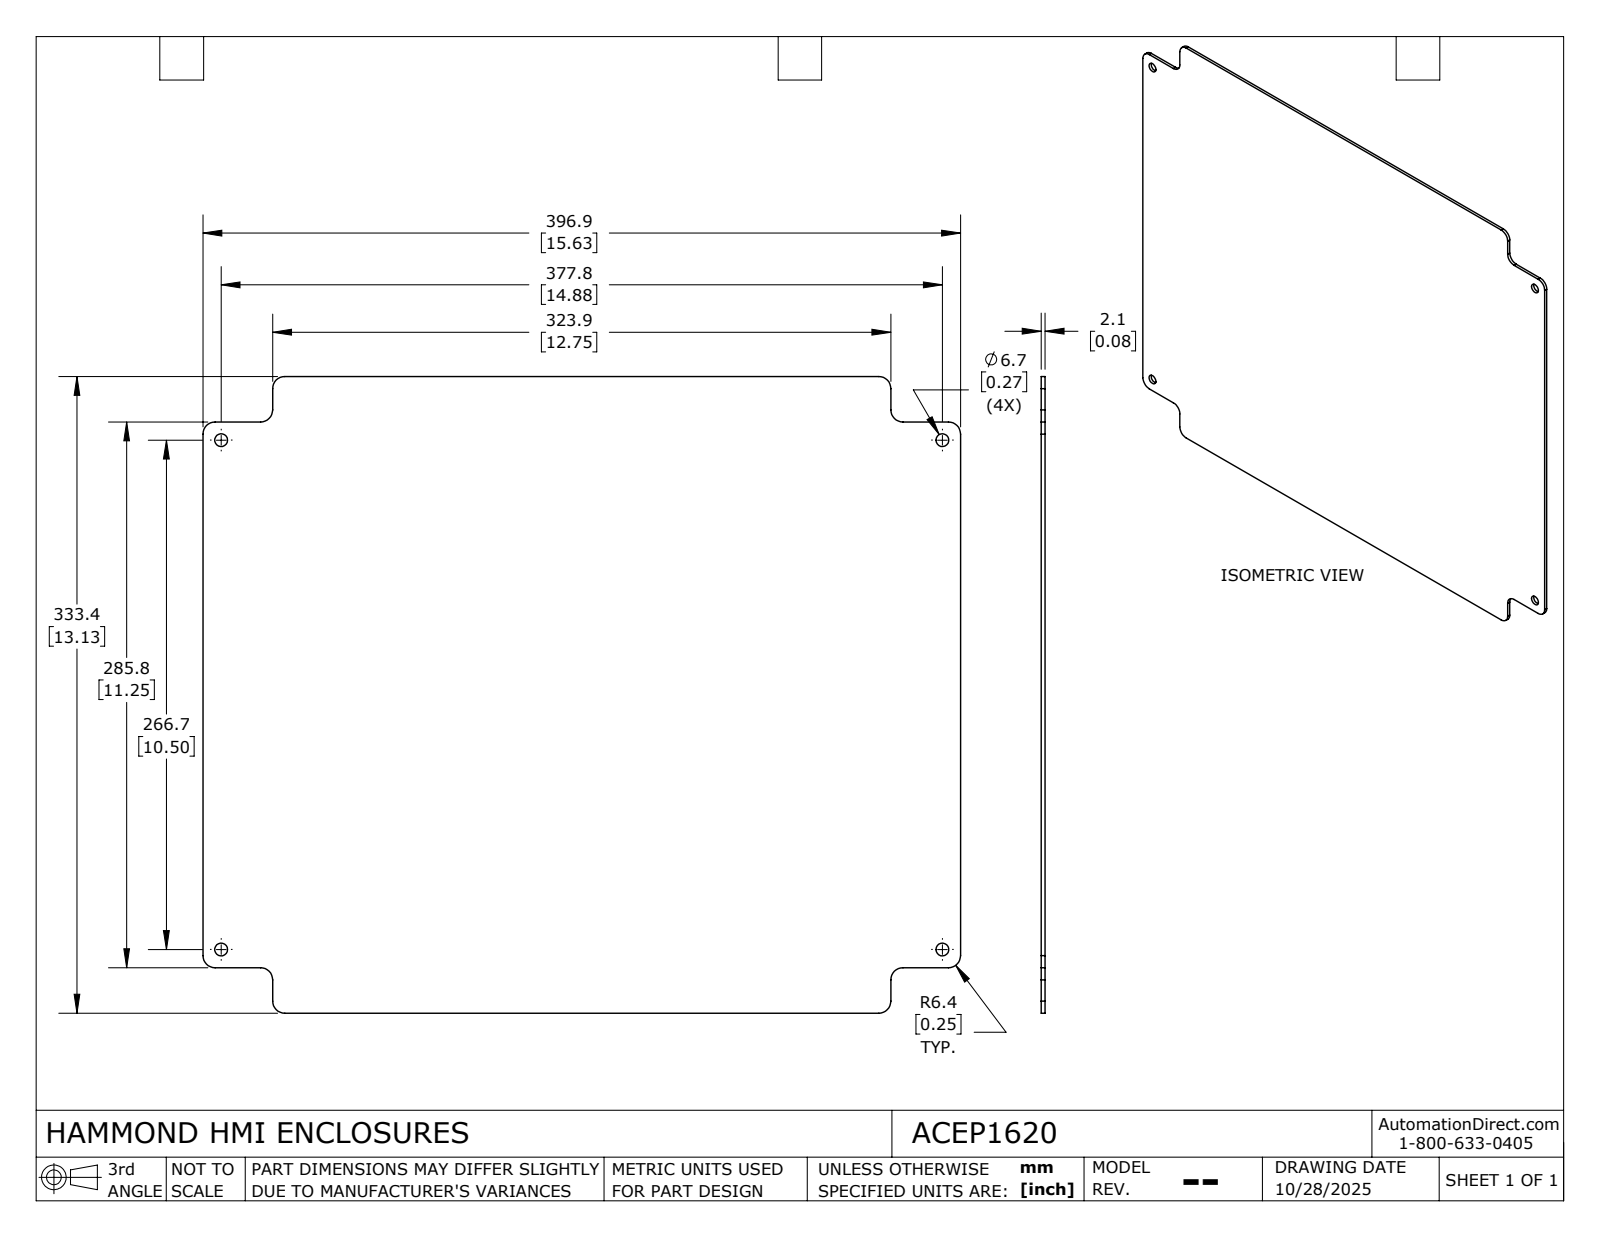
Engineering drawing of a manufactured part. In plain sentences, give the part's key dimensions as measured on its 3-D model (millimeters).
The part is named "ACEP1620". Its 3-D file was written by "SolidWorks 2024 (AUTOMOTIVE_DESIGN)". It is 1 solid with 30 faces: 14 planar, 16 cylindrical and 0 other. Overall it measures 396.88 by 333.38 by 2.06 millimeters. Its volume is 264 692 cubic millimeters and its surface area 260 418 square millimeters. Round holes: 4 of diameter 6.73. Partial cylindrical surfaces (rounded edges, fillets, slot ends): 12 of radius 6.35. The main face-to-face distances are 2.06, 333.38, 396.88, 23.81, 309.57, 285.76, 36.51, 360.37, 323.86. The hole center spacings are 266.7, 377.82, 462.47.
